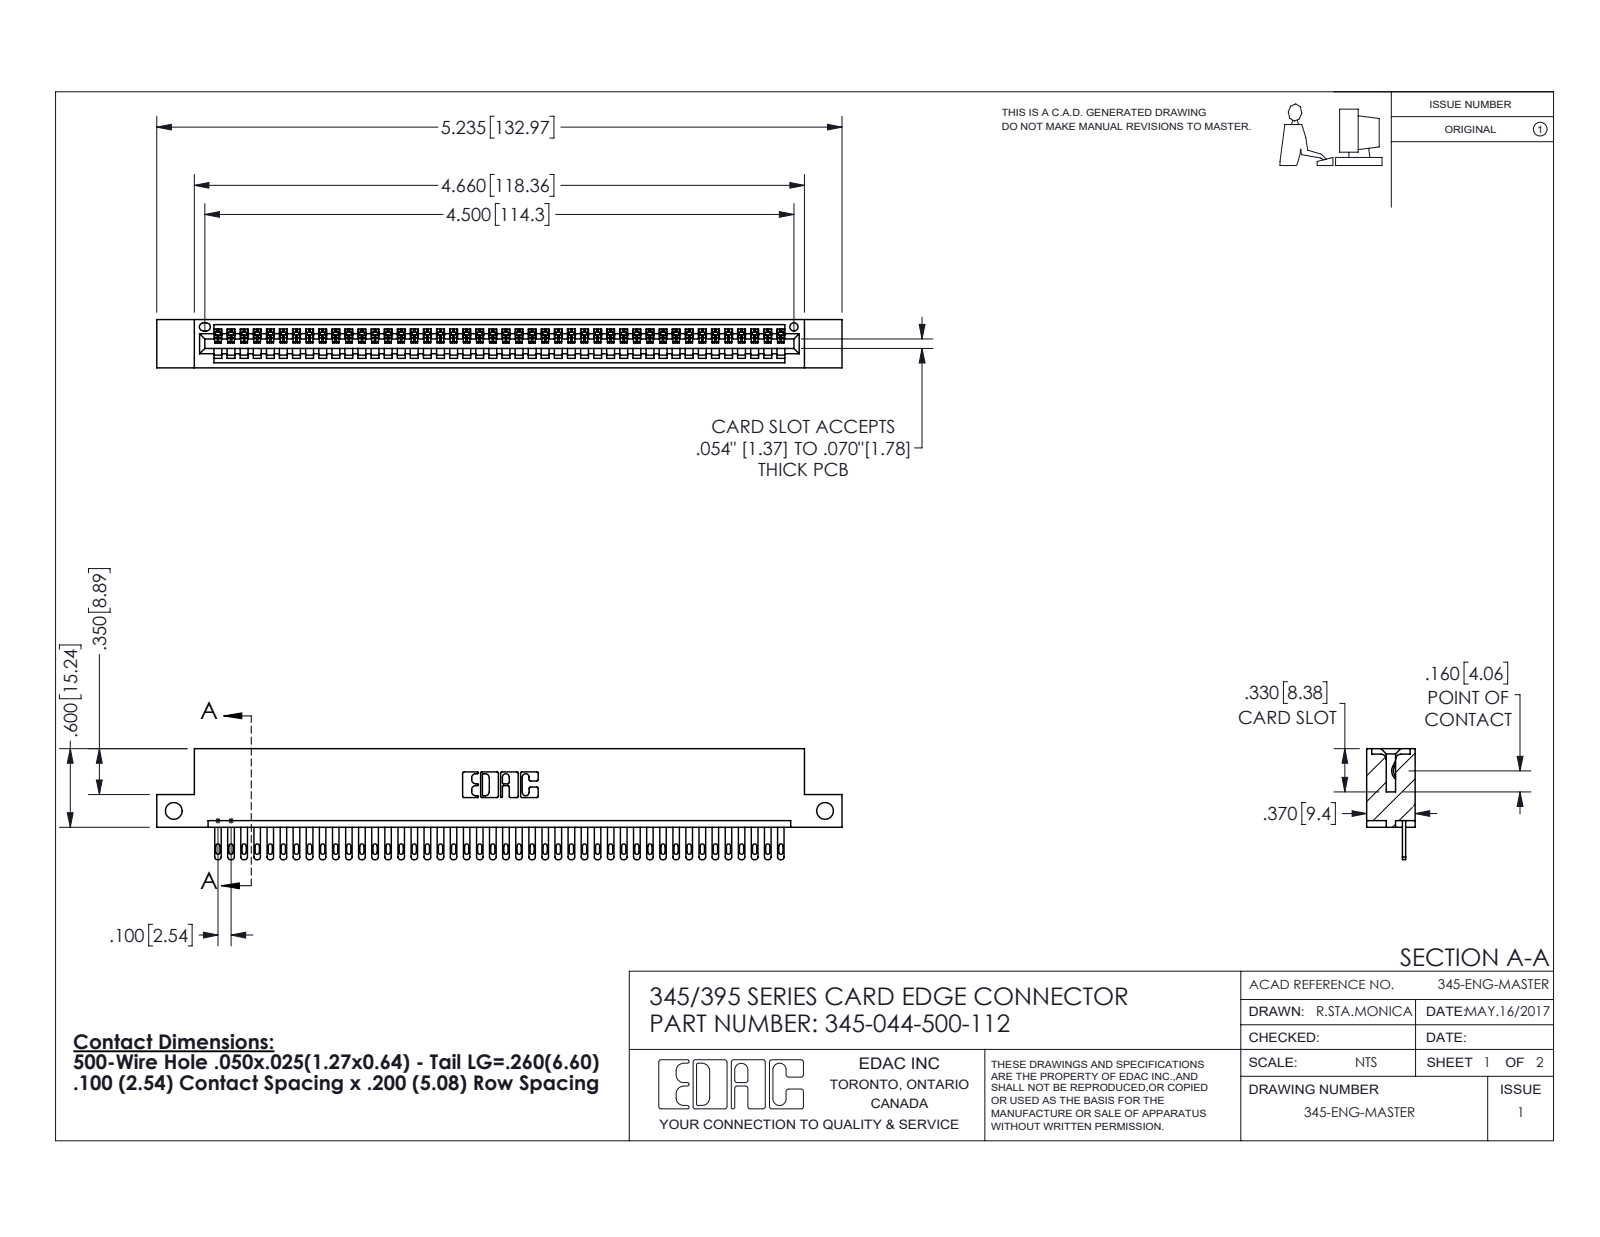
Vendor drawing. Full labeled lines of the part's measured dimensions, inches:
Part name (STEP PRODUCT): 345-044-500-112; 345 Part_Flush Mounting Lugs - Side Mount; 345-292-001_345-293-100
STEP written by: SolidWorks 2016 (CONFIG_CONTROL_DESIGN)
Units: inches
Bodies: 45 solids, 2502 faces (1576 planar, 926 cylindrical, 0 other)
Overall size (bounding box): 5.235 × 0.847 × 0.37
Volume: 0.768 in³ · Surface area: 25.9 in²
Round holes (diameter × count): ⌀0.128 ×2, ⌀0.064 ×1
Partial cylindrical surfaces — rounded edges, fillets, slot ends (radius × count): R0.006 ×88, R0.016 ×88, R0.02 ×88, R0.01 ×22, R0.007 ×6, R0.031 ×6, R0.026 ×3, R0.031 ×2
Main face-to-face distances: 0.298, 0.072, 0.37, 0.2, 0.098, 0.272, 0.025, 0.225, 0.149, 0.072
Hole centre spacings: 4.975
